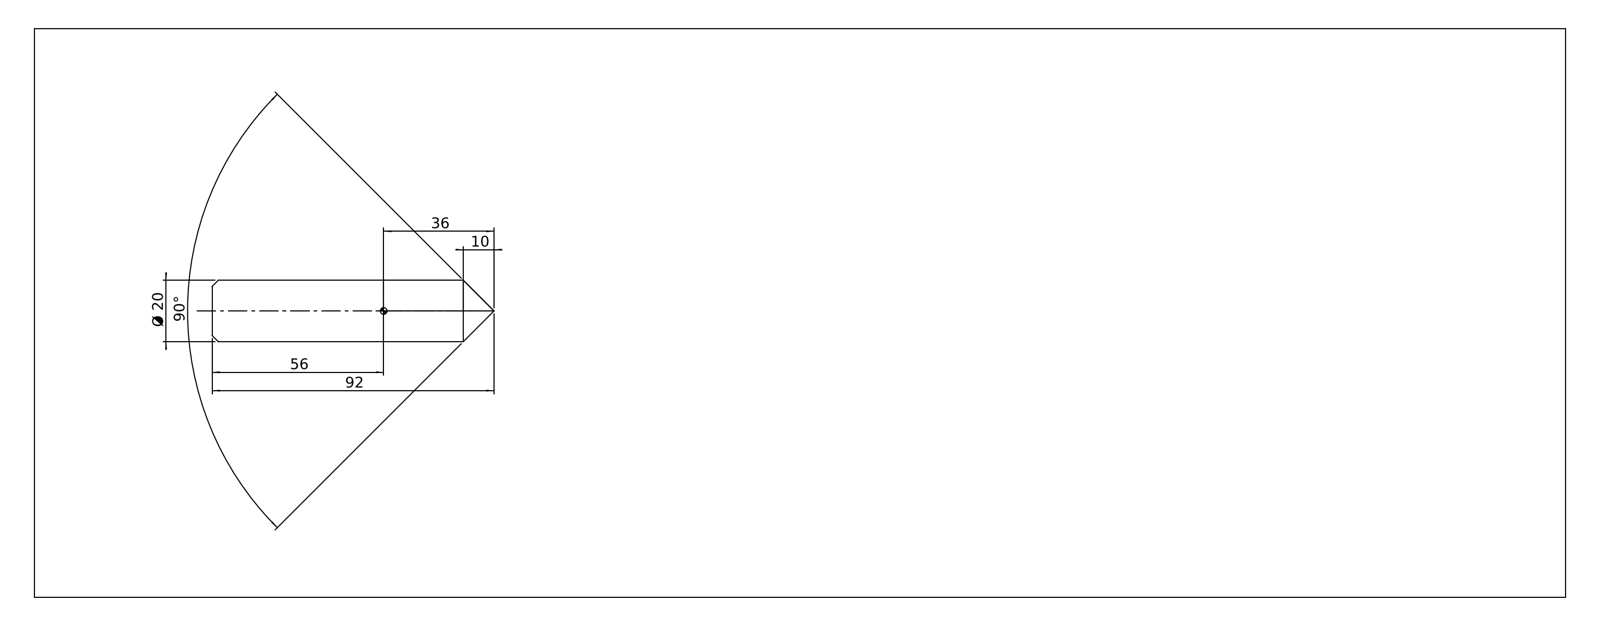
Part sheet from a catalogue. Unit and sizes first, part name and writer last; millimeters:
Units: millimetres
Overall size (bounding box): 92 × 20 × 20
Round bosses / shafts (diameter × count): ⌀20 ×1
Main face-to-face distances: 82
Volume: 26 691 mm³ · Surface area: 6 460 mm²
Bodies: 2 solids, 6 faces (3 planar, 1 cylindrical, 2 other)
Part name (STEP PRODUCT): 890.200.00
STEP written by: SolidWorks 2019 (CONFIG_CONTROL_DESIGN)
